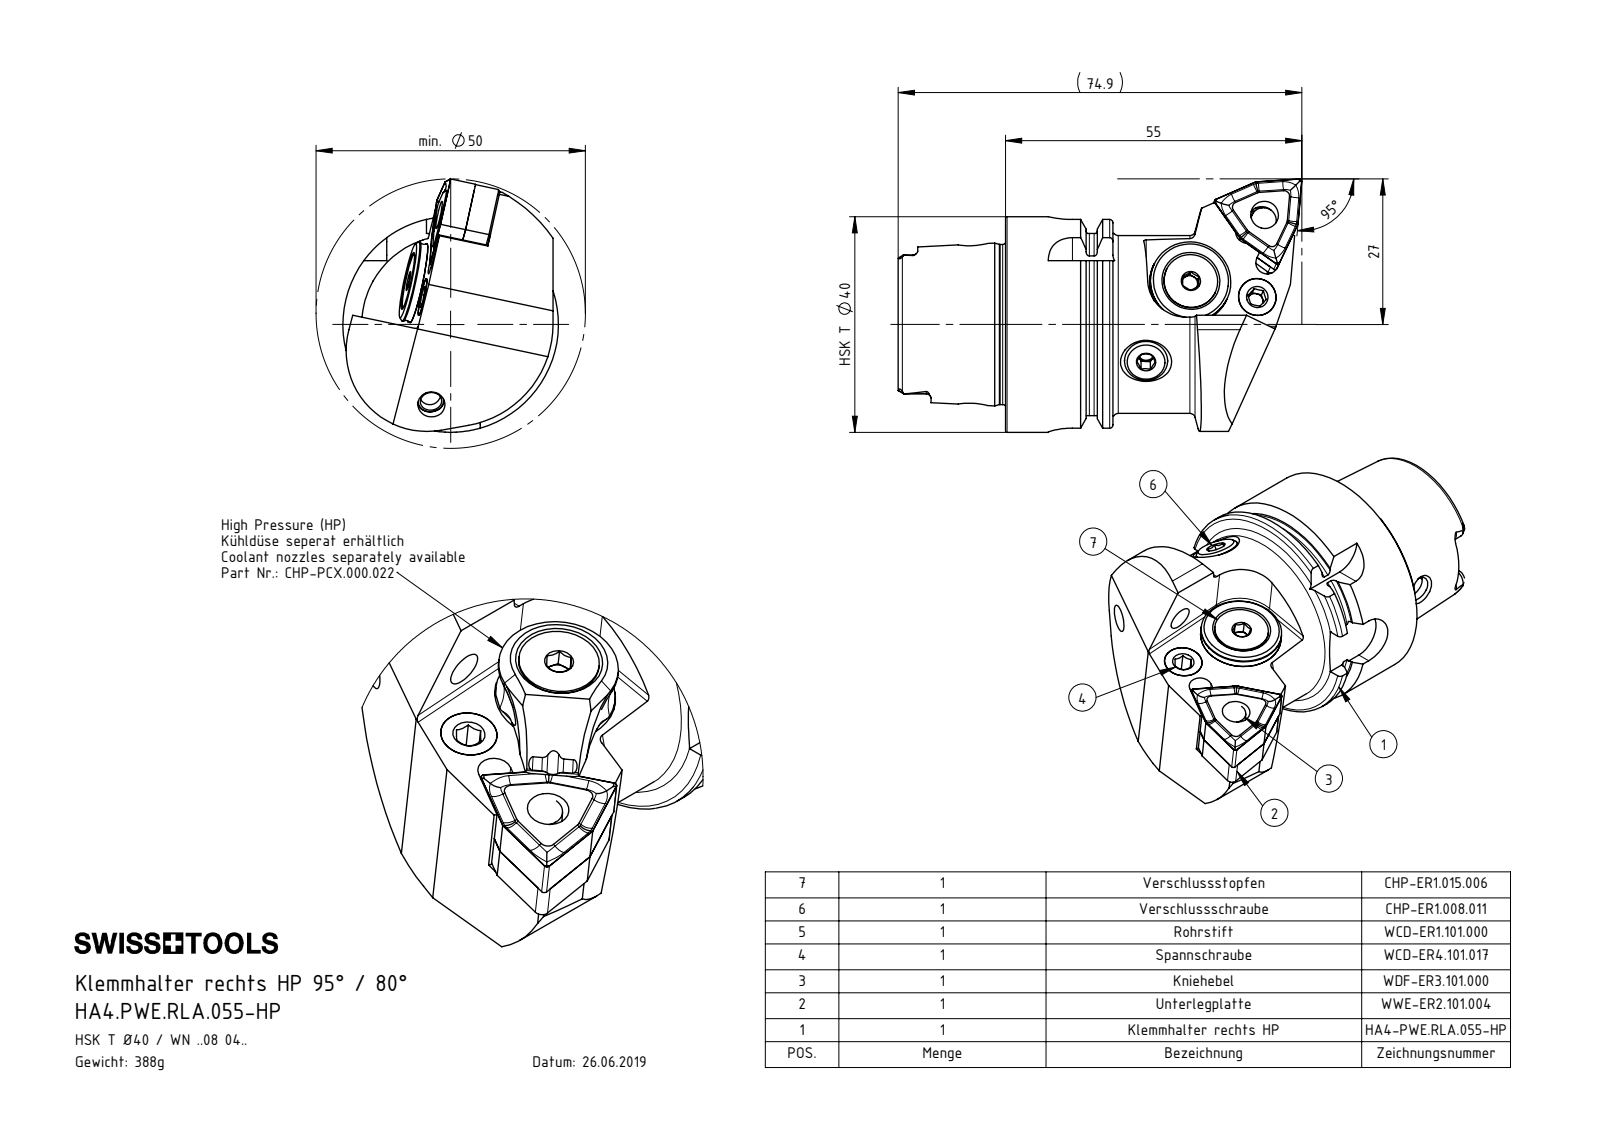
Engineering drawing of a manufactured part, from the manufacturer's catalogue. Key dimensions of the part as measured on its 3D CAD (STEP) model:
Part name (STEP PRODUCT): KVT_MB_600_050; ISO 8752 2x8; WCD-ER4.101.017_A; CHP-PCX.000.022_Dse (+8 more)
STEP written by: SolidWorks 2017 (AUTOMOTIVE_DESIGN)
Units: millimetres
Bodies: 15 solids, 435 faces (117 planar, 103 cylindrical, 215 other)
Overall size (bounding box): 54.7 × 47 × 40
Volume: 4 750 mm³ · Surface area: 6 892 mm²
Round holes (diameter × count): ⌀4 ×2, ⌀1.2 ×1, ⌀3 ×1, ⌀5.16 ×1, ⌀5.3 ×1, ⌀6.7 ×1, ⌀7.8 ×1, ⌀13 ×1
Round bosses / shafts (diameter × count): ⌀5 ×3, ⌀8 ×2, ⌀40 ×1, ⌀14.85 ×1, ⌀13.4 ×1, ⌀10 ×1, ⌀7.9 ×1, ⌀6.4 ×1
Partial cylindrical surfaces — rounded edges, fillets, slot ends (radius × count): R1 ×10, R0.4 ×3, R6 ×3, R0.5 ×2, R1.1 ×2, R1.2 ×2, R5 ×2, R22.9 ×2
Main face-to-face distances: 4.76, 6.22, 1.46, 6.3, 11.06, 12.52, 4, 4.7, 8.7, 3
Hole centre spacings: 4.51, 15.97, 19.18
